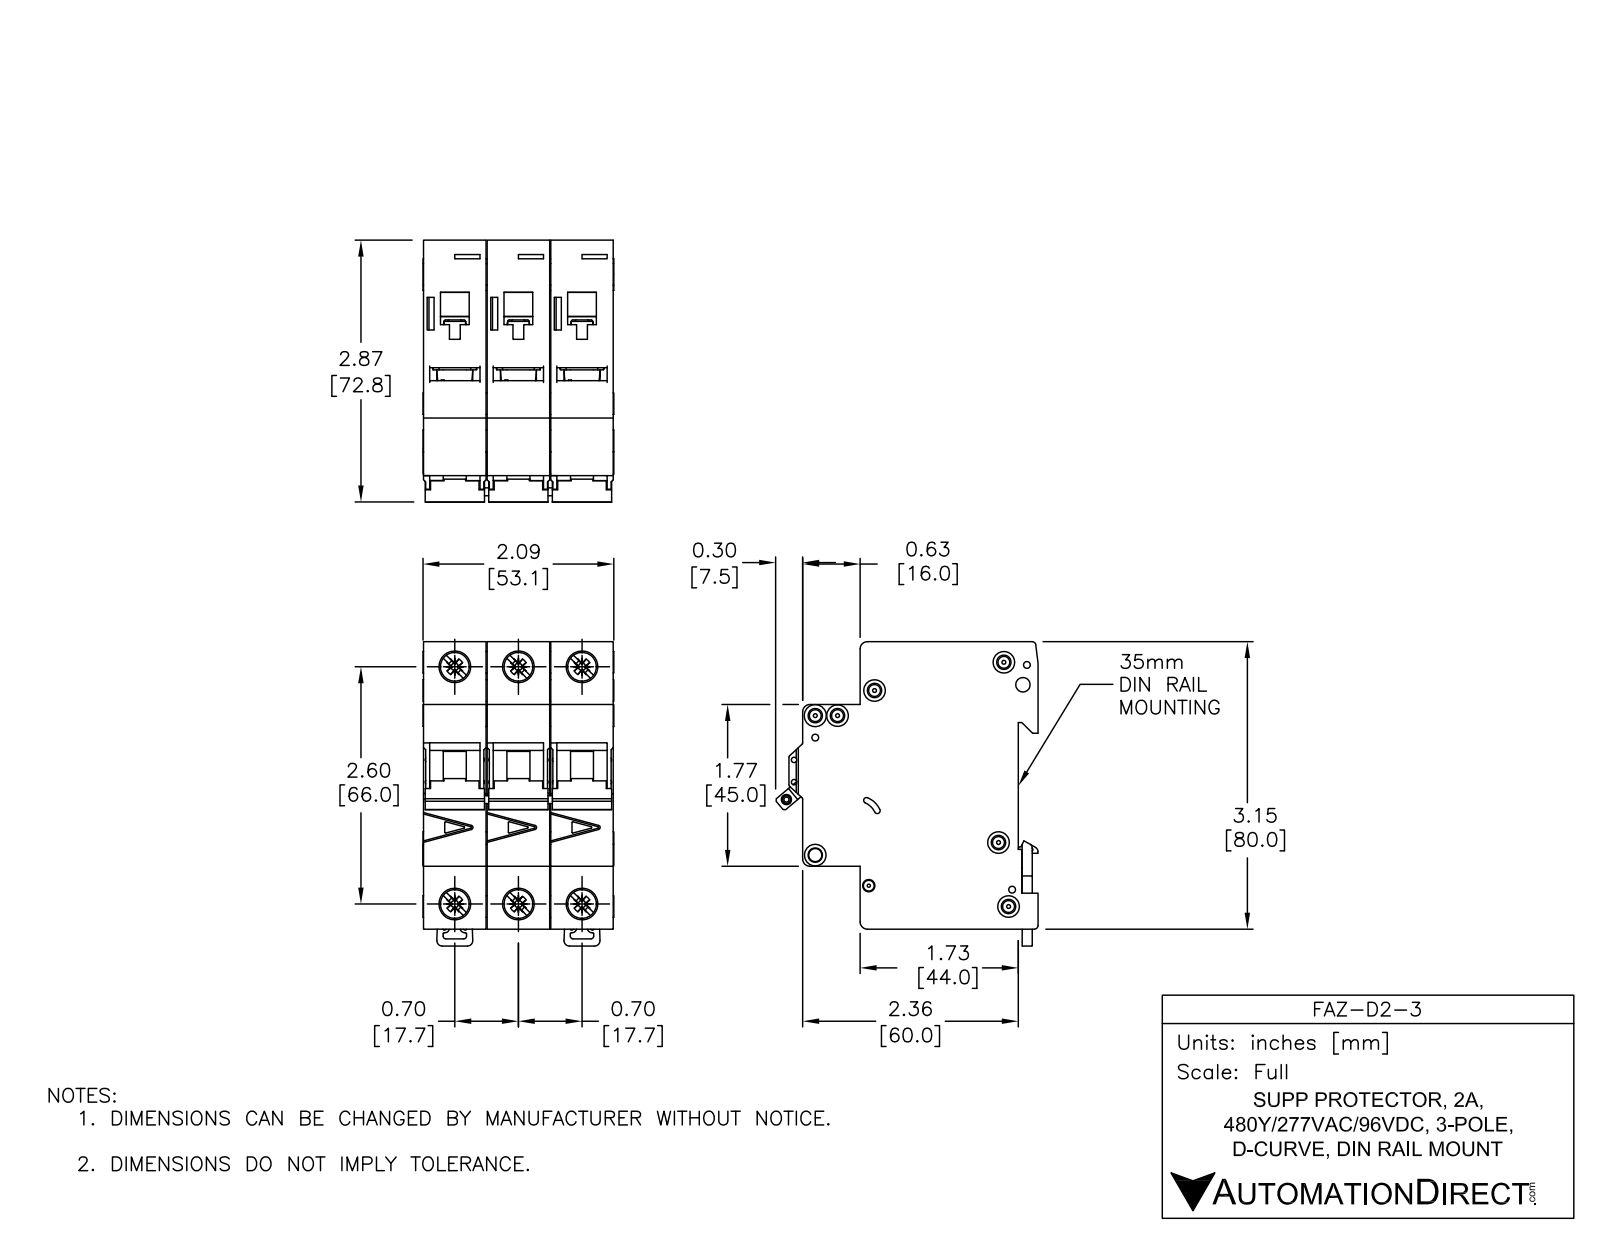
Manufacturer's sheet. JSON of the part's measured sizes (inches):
{"part_name": "FAZ-D2-3", "step_written_by": "SolidWorks 2014 (AUTOMOTIVE_DESIGN)", "units": "inches", "bodies": {"solids": 11, "faces": 1650, "planar": 697, "cylindrical": 590, "other": 363}, "overall_size": [3.338, 2.876, 2.091], "volume_in3": 13.71, "surface_area_in2": 89.98, "round_holes": [[0.142, 6], [0.323, 4], [0.075, 3], [0.043, 2], [0.059, 2], [0.157, 2], [0.281, 2], [0.085, 1], [0.087, 1], [0.1, 1], [0.13, 1], [0.134, 1]], "round_bosses_or_shafts": [[0.236, 4], [0.098, 3], [0.323, 2]], "partial_cylinders_radius": [[0.01, 68], [0.02, 25], [0.039, 12], [0.079, 12], [0.008, 11], [0.071, 3], [0.031, 2], [0.118, 2]], "face_to_face_distances": [0.697, 0.689, 1.394, 1.386, 2.083, 0.705, 3.129, 0.217, 1.949, 1.732], "hole_center_spacings": [0.697, 2.69, 2.598, 0.244, 0.537, 1.394, 2.948, 0.189]}
